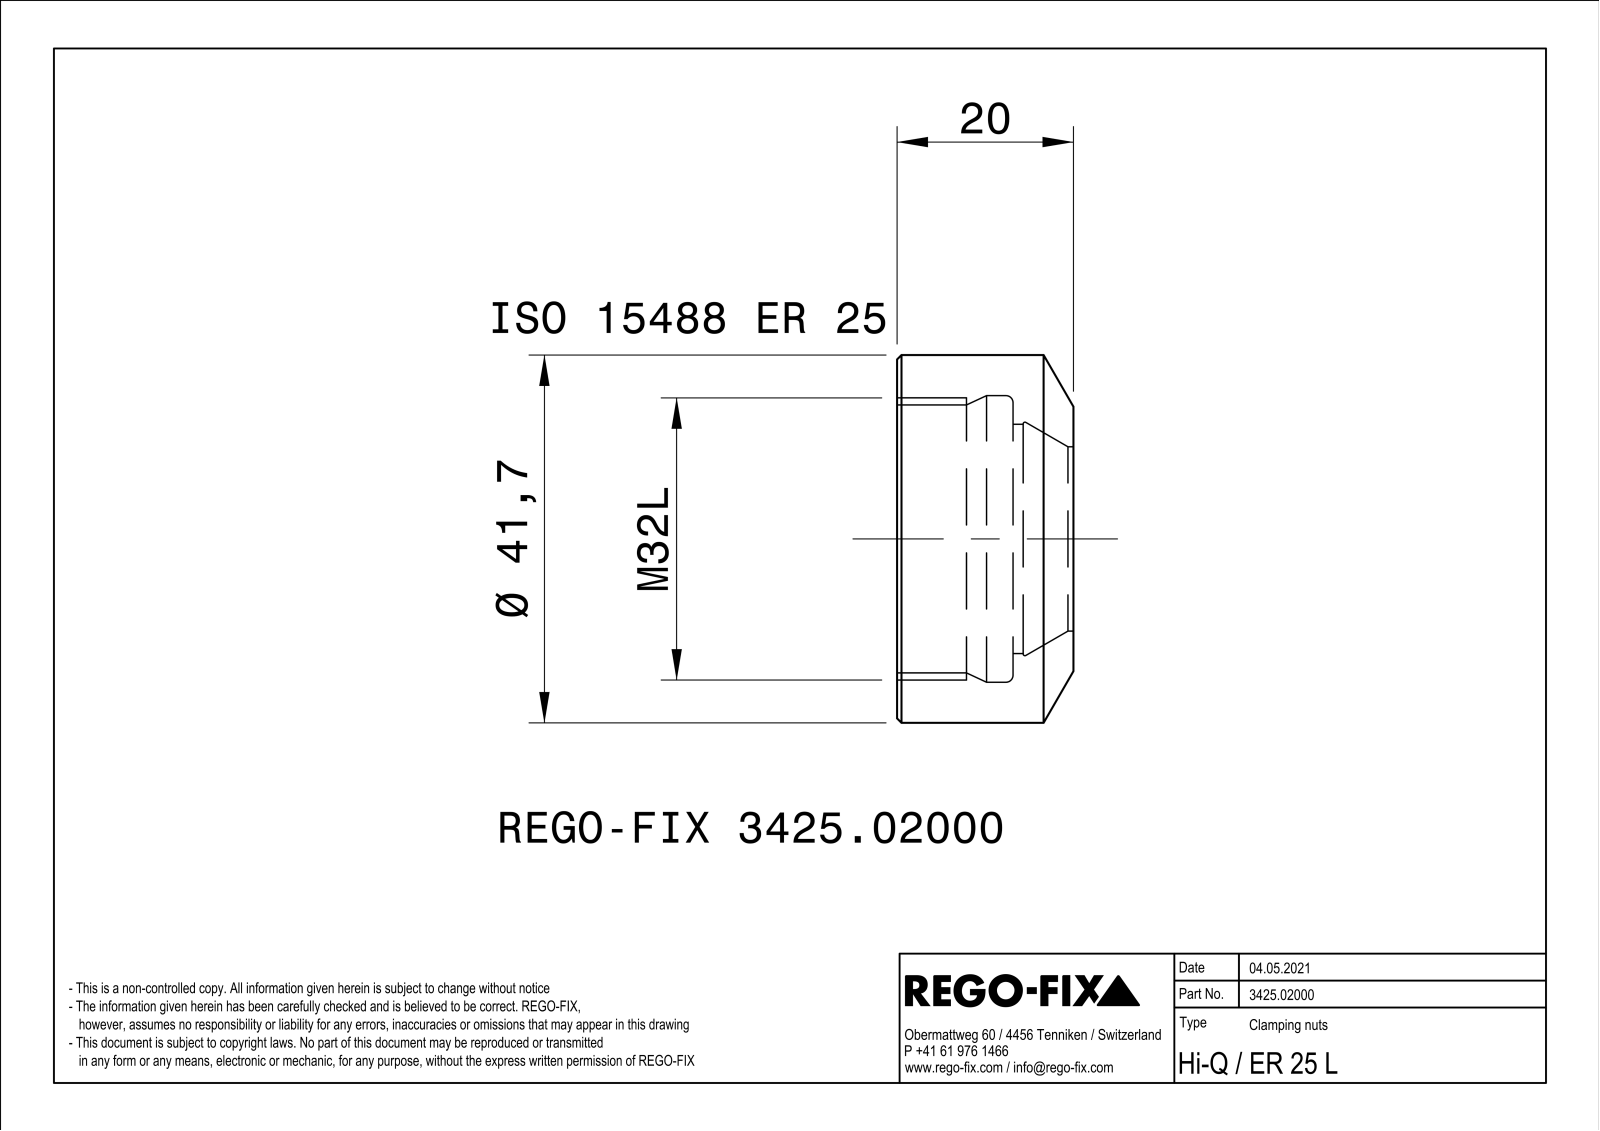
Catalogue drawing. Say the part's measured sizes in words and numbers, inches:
The part is named "NOCUT". Its 3-D file was written by "SIEMENS PLM Software Solid Edge ST10 (AUTOMOTIVE_DESIGN)". It is 1 solid with 63 faces: 34 planar, 5 cylindrical and 24 other. Overall it measures 1.642 by 1.642 by 0.787 inches. Its volume is 0.741 cubic inches and its surface area 9.725 square inches. Round holes: 1 of diameter 0.823, 1 of diameter 1.024, 1 of diameter 1.196, 1 of diameter 1.28. Round bosses or shafts: 1 of diameter 1.642. The main face-to-face distances are 0.787, 0.27, 0.518, 1.417, 0.192, 0.191, 1.177, 1.178, 0.224, 0.045.
